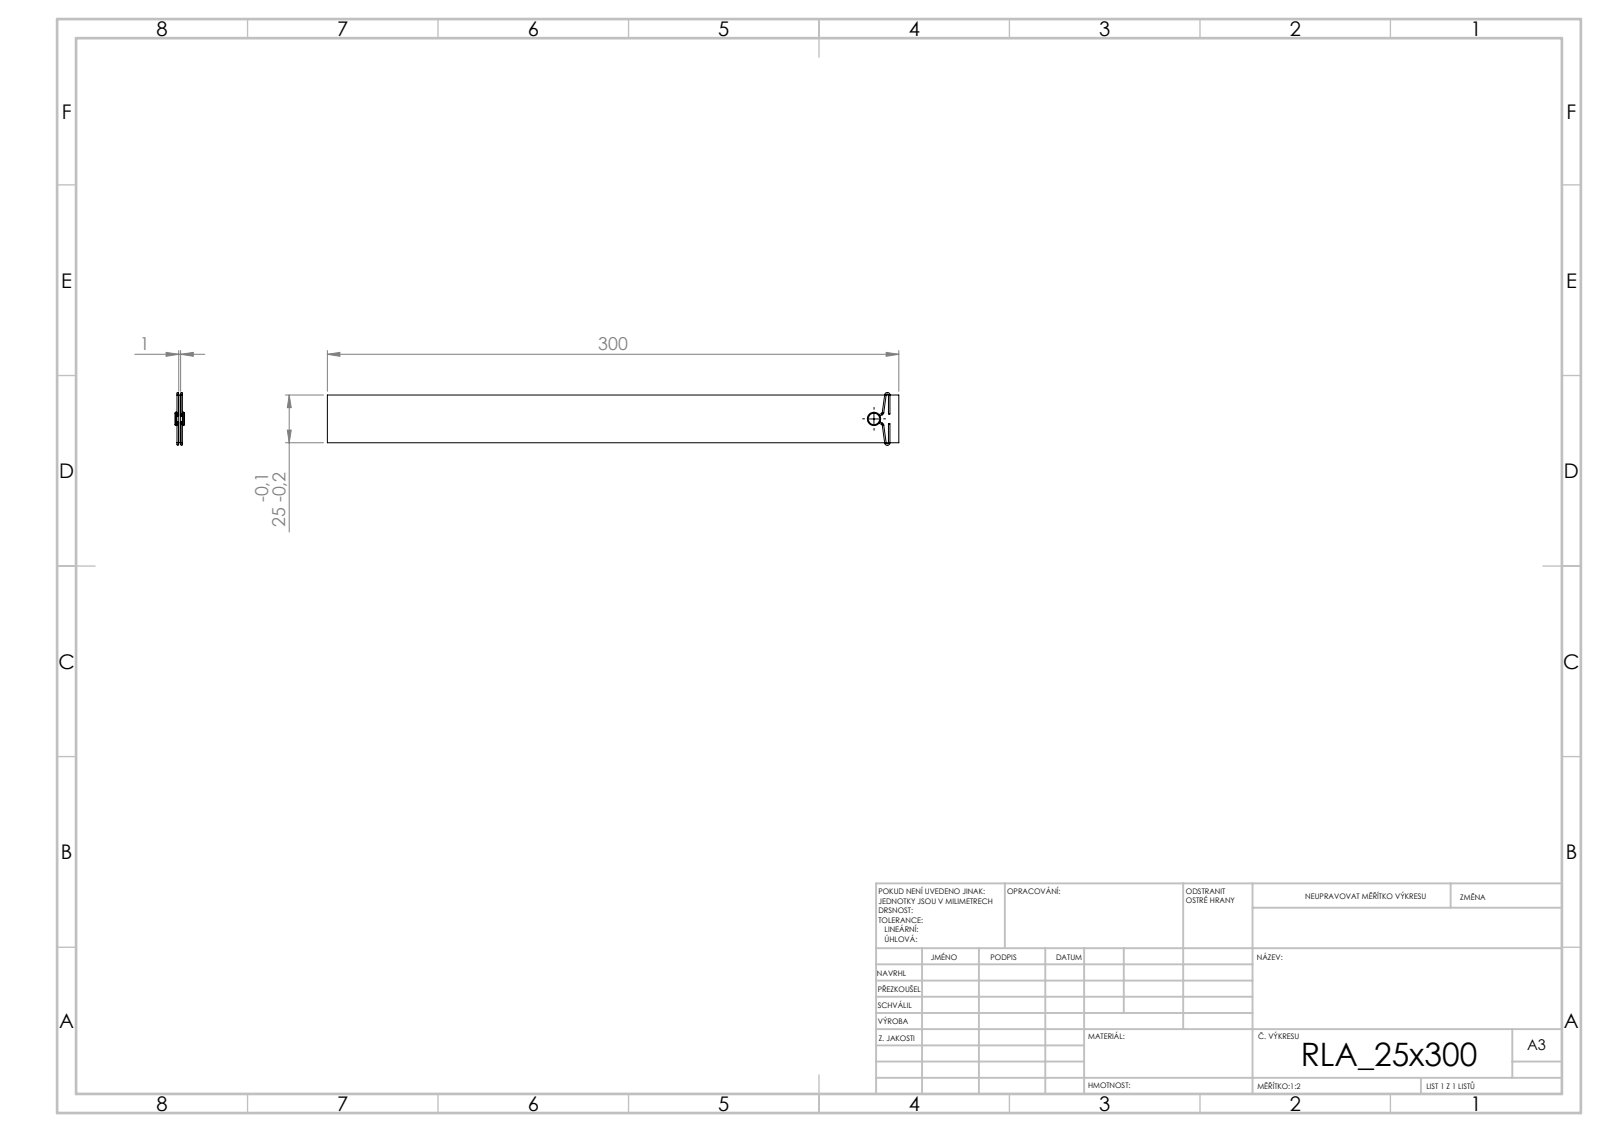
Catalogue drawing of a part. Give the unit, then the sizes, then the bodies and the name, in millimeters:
Units: millimetres
Overall size (bounding box): 300 × 27.8 × 5
Round bosses / shafts (diameter × count): ⌀0.8 ×14, ⌀7 ×1, ⌀4 ×1
Main face-to-face distances: 1, 25, 2, 3, 4, 5, 300, 9.95, 15.05, 5.1
Volume: 7 664 mm³ · Surface area: 16 135 mm²
Bodies: 3 solids, 82 faces (14 planar, 40 cylindrical, 28 other)
STEP written by: SolidWorks 2019 (CONFIG_CONTROL_DESIGN)
